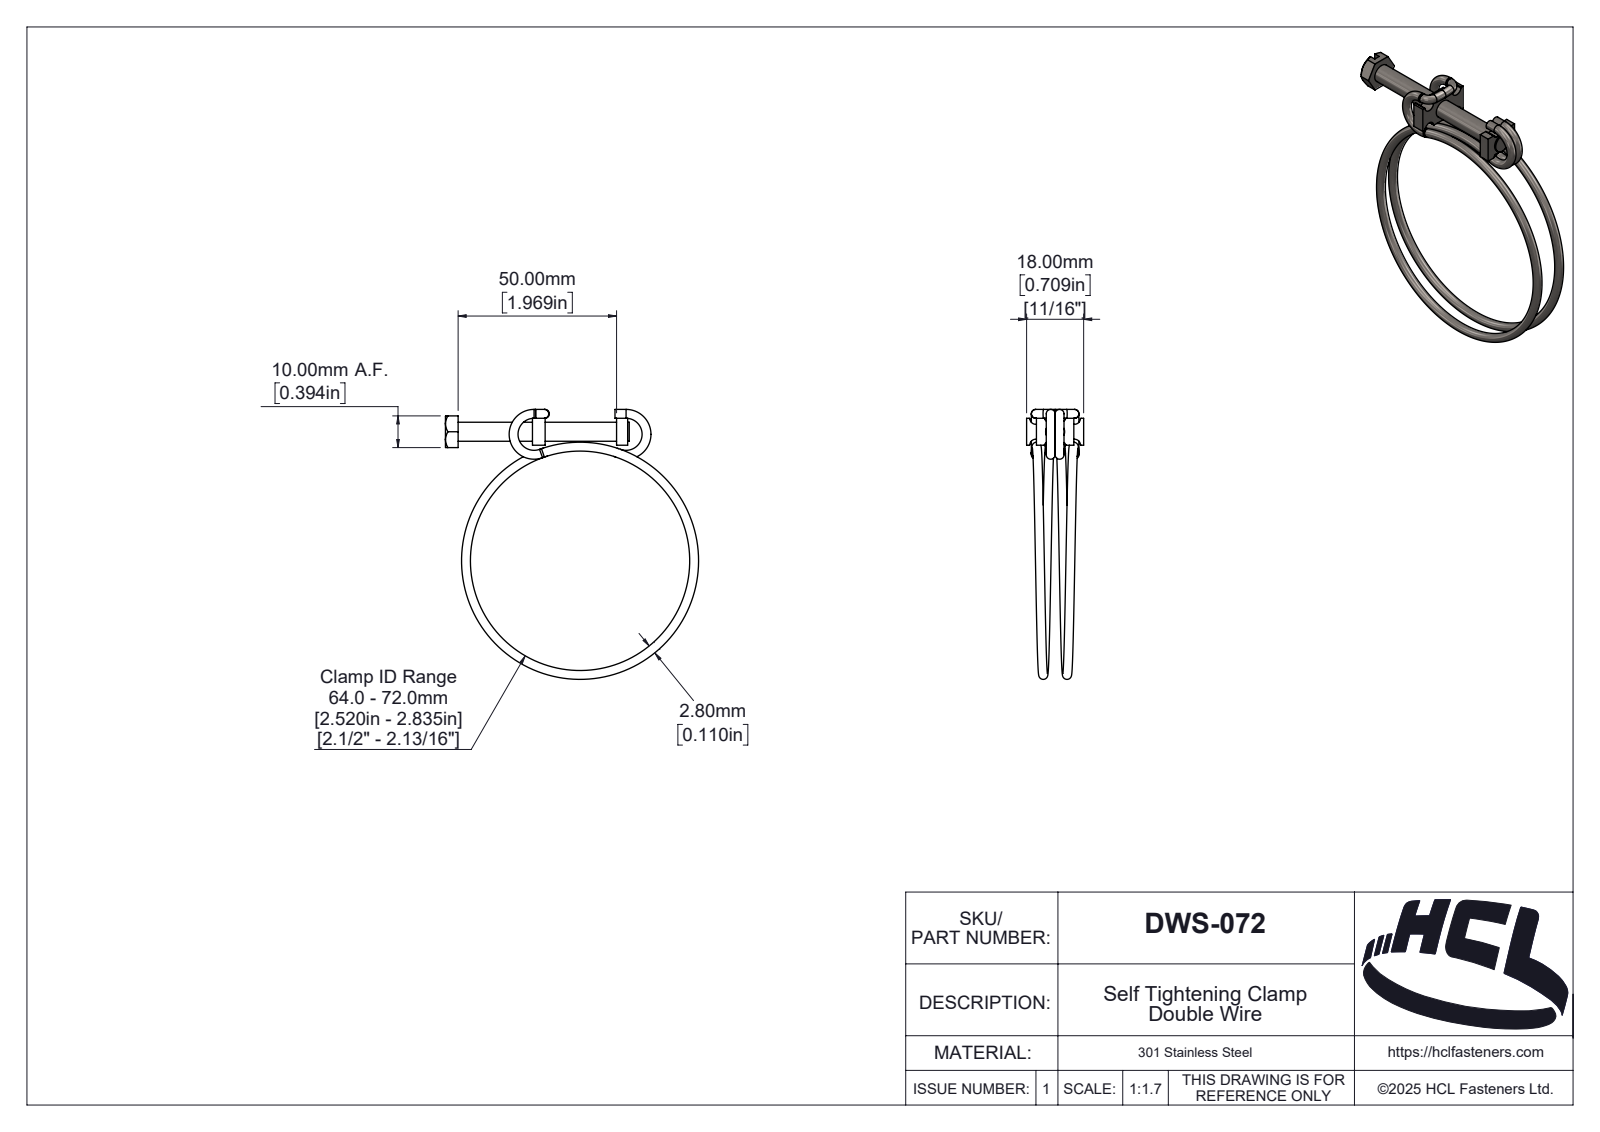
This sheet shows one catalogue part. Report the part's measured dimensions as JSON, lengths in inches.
{"part_name": "DWS-072", "step_written_by": "SolidWorks 2025 (AUTOMOTIVE_DESIGN)", "units": "inches", "bodies": {"solids": 6, "faces": 213, "planar": 55, "cylindrical": 74, "other": 84}, "overall_size": [3.352, 3.145, 0.709], "volume_in3": 0.381, "surface_area_in2": 11.89, "round_holes": [[0.236, 1]], "round_bosses_or_shafts": [[0.11, 4]], "partial_cylinders_radius": [[0.008, 12], [0.039, 4], [0.075, 4], [0.016, 1], [0.02, 1], [0.021, 1], [0.025, 1], [0.036, 1]], "face_to_face_distances": [0.157, 1.081, 0.394, 1.045, 2.126, 1.025, 2.106, 0.079, 1.183, 0.887]}
